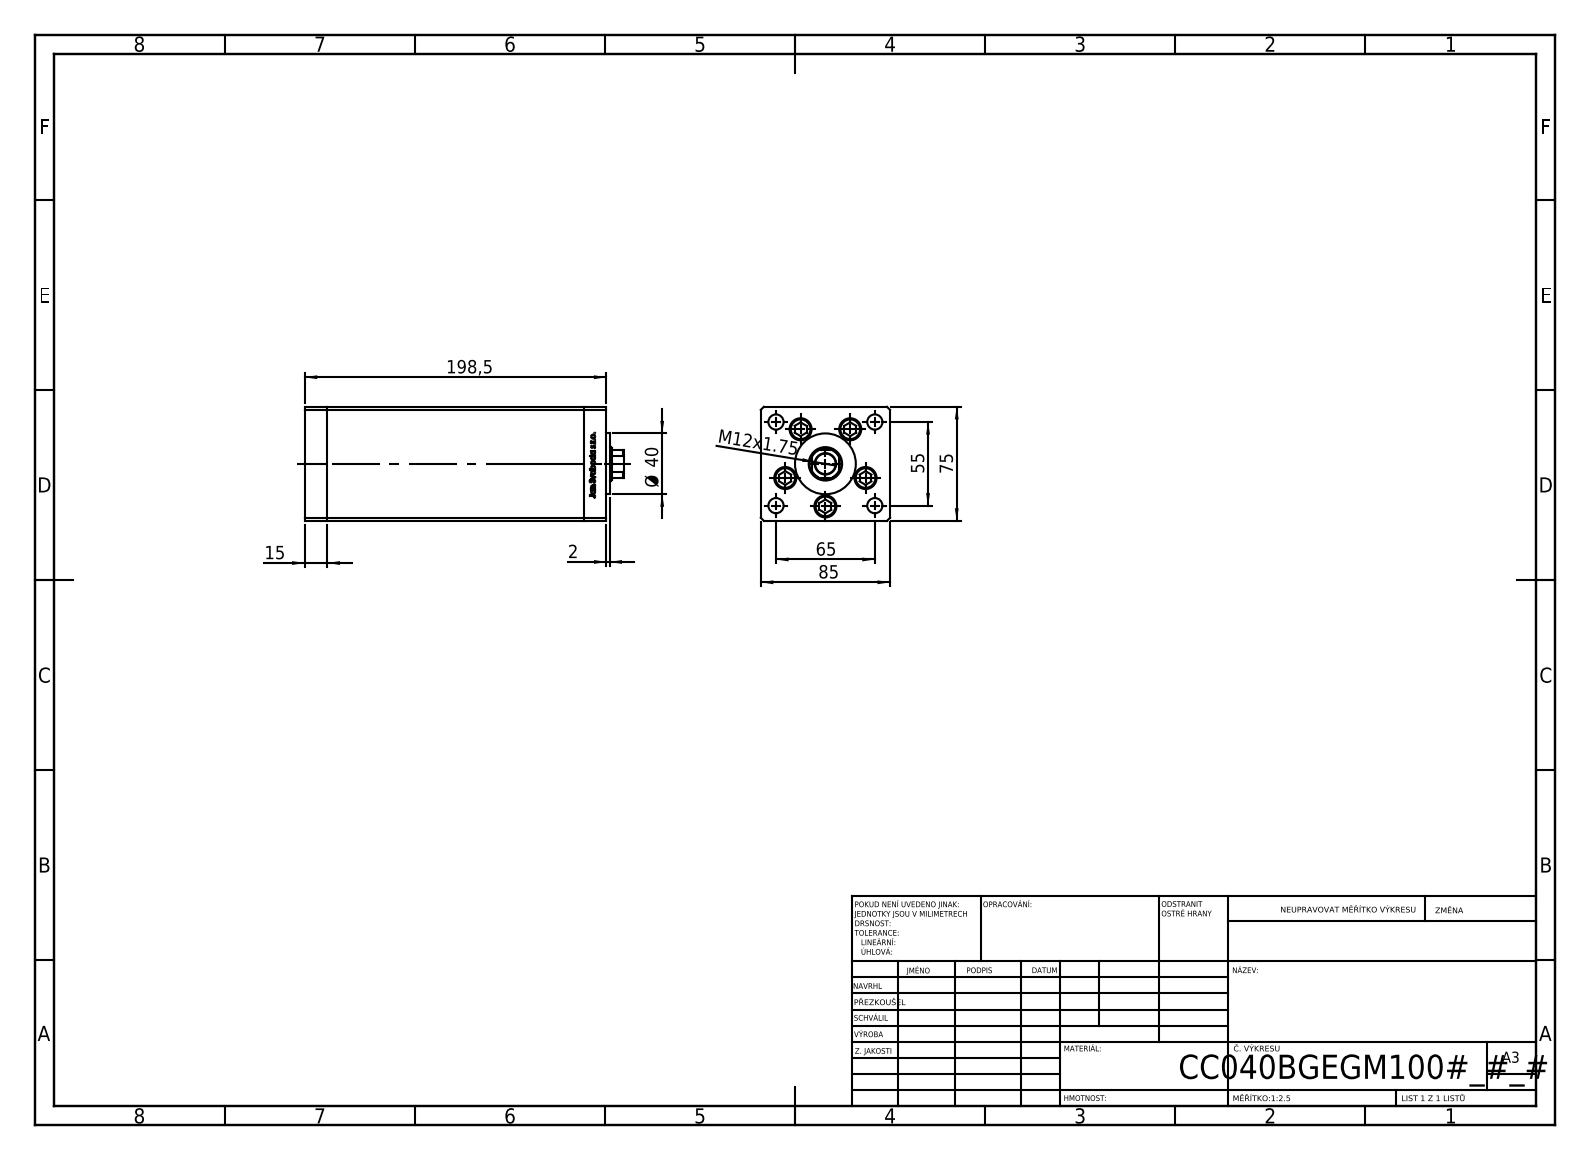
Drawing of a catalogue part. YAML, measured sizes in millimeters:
part_name: "V220C_B MIDDLE; ALLEN BOLT; V220C BACK_B; V220C_VC_B (+1 more)"
step_written_by: "SolidWorks 2019 (CONFIG_CONTROL_DESIGN)"
units: millimeters
bodies: {solids: 14, faces: 1185, planar: 464, cylindrical: 147, other: 574}
overall_size: [210, 85, 75]
volume: 1118000
surface_area: 171182
round_holes:
  - {diameter: 11, count: 5}
  - {diameter: 14.5, count: 5}
  - {diameter: 10, count: 4}
  - {diameter: 2, count: 2}
  - {diameter: 13.16, count: 2}
  - {diameter: 13.5, count: 1}
  - {diameter: 22, count: 1}
round_bosses_or_shafts:
  - {diameter: 8, count: 5}
  - {diameter: 40, count: 1}
partial_cylinders:
  - {radius: 0.93, count: 2}
  - {radius: 10.5, count: 1}
face_to_face_distances: [85, 75, 15, 168.5, 183.5, 198.5, 34.25, 68.5, 19.25, 149.25]
hole_center_spacings: [28, 42.57, 16.86, 19.17, 32.33, 32.5, 33.63, 37.33]
